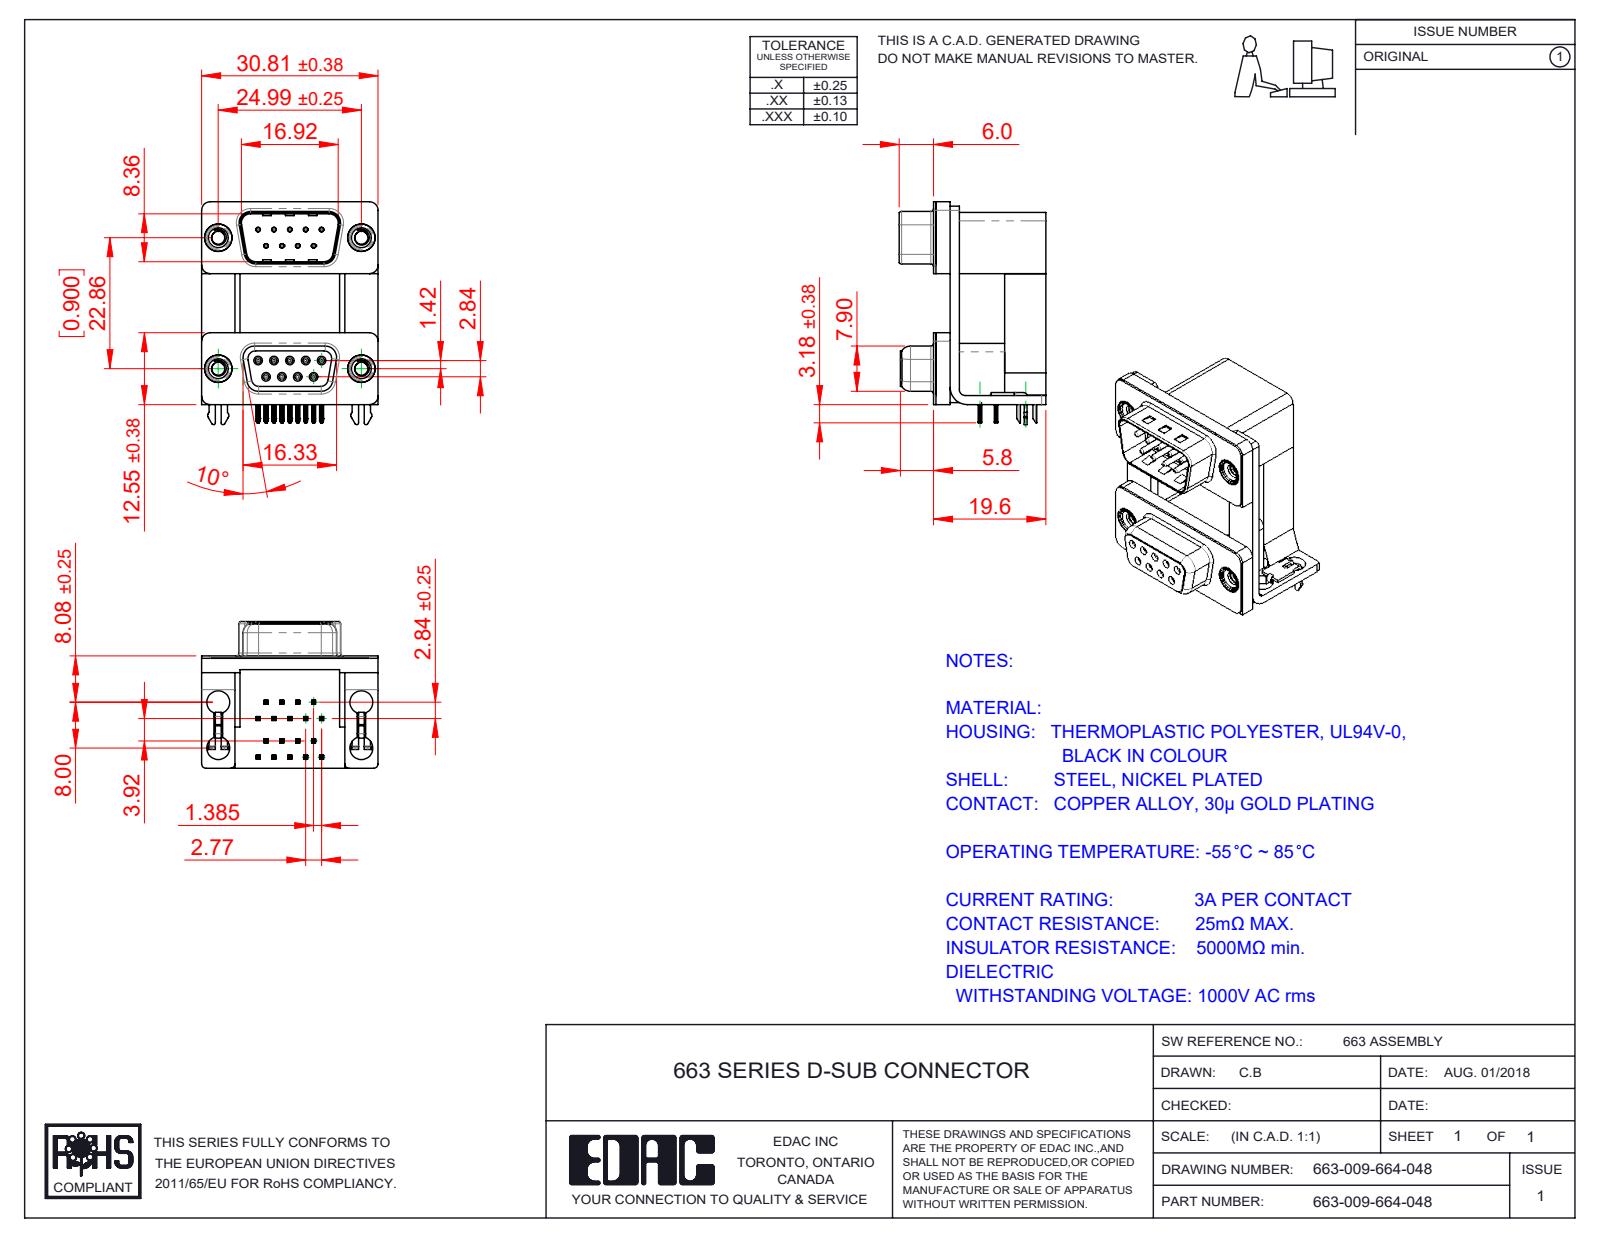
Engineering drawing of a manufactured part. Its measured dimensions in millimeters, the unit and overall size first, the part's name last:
Units: millimetres
Overall size (bounding box): 38.91 × 30.81 × 25.6
Round holes (diameter × count): ⌀0.8 ×18, ⌀0.35 ×9, ⌀0.9 ×9, ⌀4 ×8, ⌀2.26 ×4, ⌀3.5 ×4, ⌀4.8 ×4, ⌀5 ×4
Round bosses / shafts (diameter × count): ⌀1.2 ×9, ⌀0.75 ×9, ⌀4.9 ×4, ⌀4.75 ×4, ⌀3.9 ×4
Partial cylindrical surfaces — rounded edges, fillets, slot ends (radius × count): R0.1 ×73, R0.25 ×42, R0.15 ×36, R0.12 ×18, R0.35 ×18, R0.5 ×16, R1.5 ×15, R0.75 ×10
Main face-to-face distances: 2.5, 0.4, 19.2, 16.7, 12, 7.2, 9.5, 1.6, 12.4, 19.6
Hole centre spacings: 3.16, 2.77, 23.03, 22.86, 5.54, 23.52, 20.07, 25.74
Volume: 11 349 mm³ · Surface area: 13 156 mm²
Bodies: 31 solids, 2637 faces (1341 planar, 725 cylindrical, 571 other)
Part name (STEP PRODUCT): 663 Housing Upper_09 Contacts H; 663 Shell Plug_09 Contacts; 663 Threaded Rivet_4-40; 663 Housing Lower_09 Contacts (+8 more)
STEP written by: SolidWorks 2020 (CONFIG_CONTROL_DESIGN)
